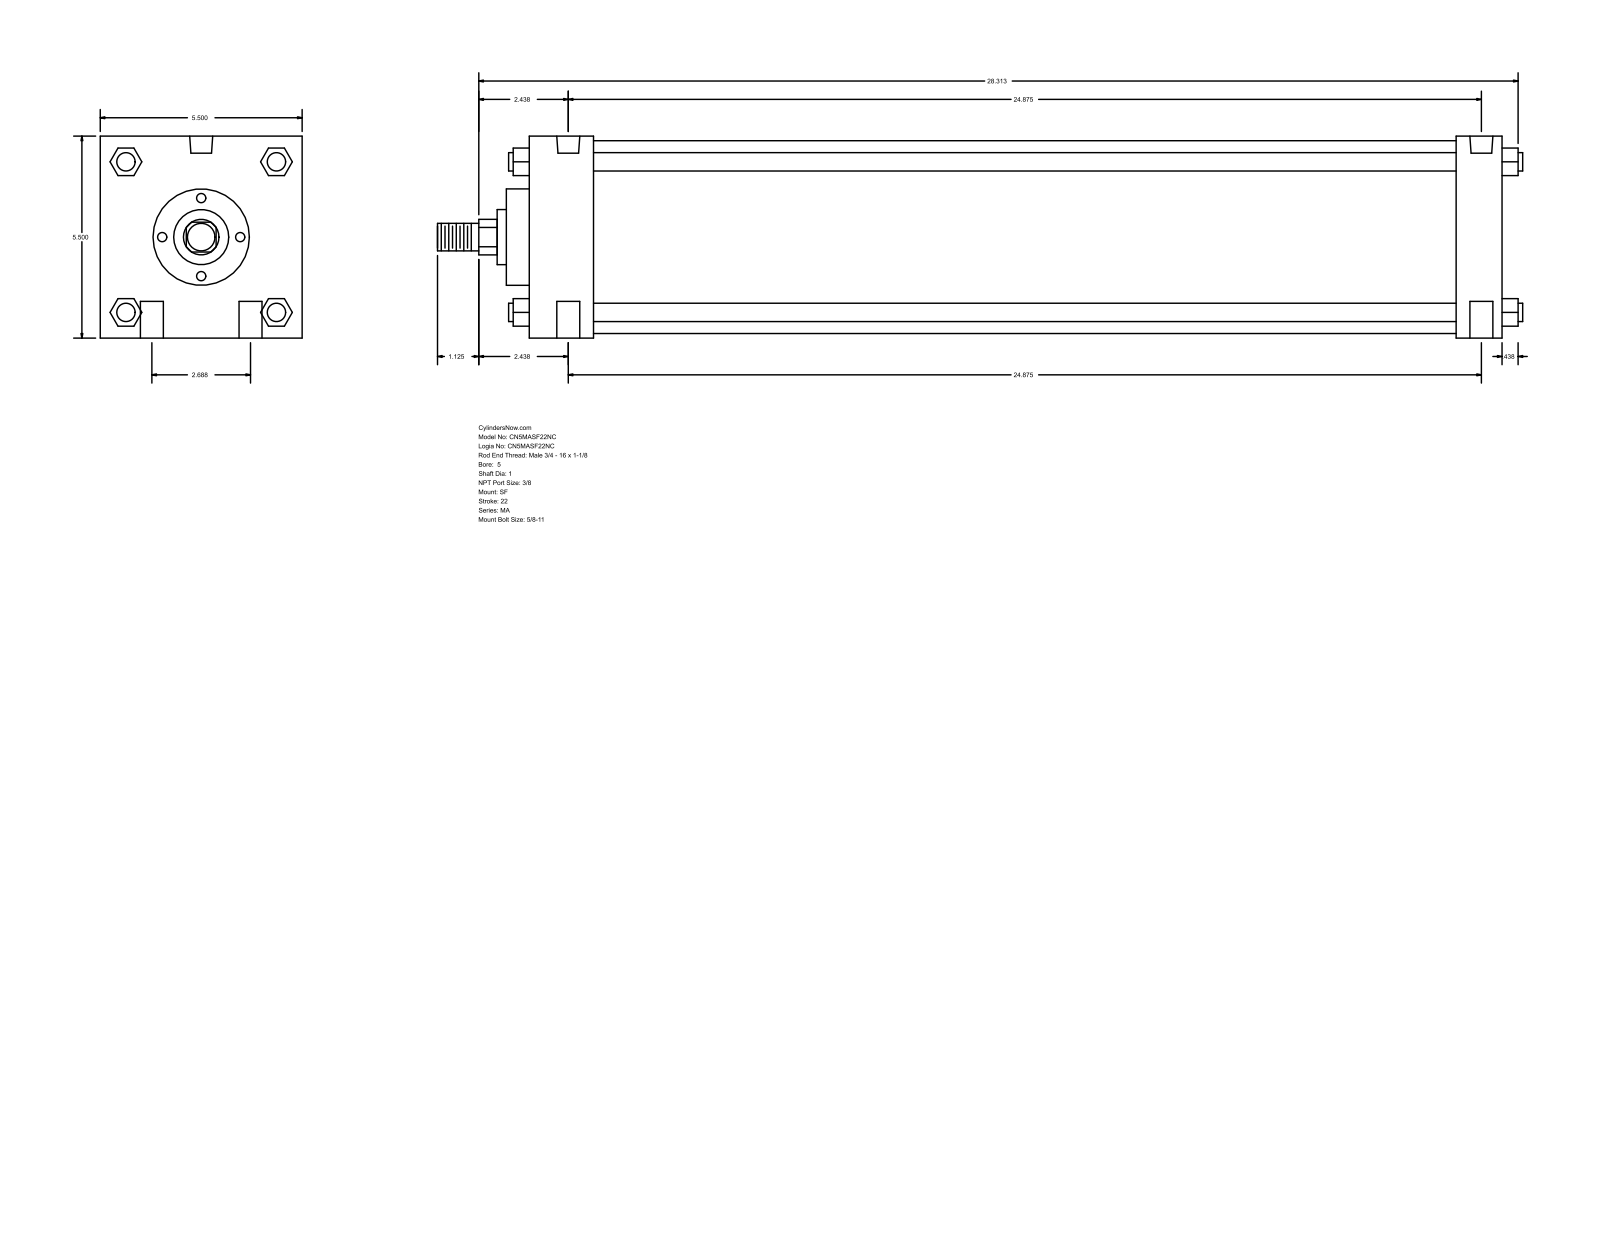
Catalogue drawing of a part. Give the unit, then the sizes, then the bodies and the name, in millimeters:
Units: millimetres
Overall size (bounding box): 750.89 × 139.7 × 139.7
Round holes (diameter × count): ⌀15.88 ×4, ⌀11.11 ×2, ⌀15.93 ×2
Round bosses / shafts (diameter × count): ⌀12.7 ×4, ⌀133.35 ×1, ⌀66.67 ×1, ⌀38.1 ×1, ⌀25.4 ×1, ⌀19.05 ×1
Partial cylindrical surfaces — rounded edges, fillets, slot ends (radius × count): R12.29 ×1
Main face-to-face distances: 139.7, 673.1, 44.46, 641.35, 596.89, 628.64, 31.75, 15.87, 60.33, 657.22
Hole centre spacings: 34.13, 632.75, 631.83, 68.26, 635.51, 622.31
Bodies: 0 solids, 126 faces (95 planar, 31 cylindrical, 0 other)
Part name (STEP PRODUCT): MA_SF__0500_1
STEP written by: GSSL Pune (CONFIG_CONTROL_DESIGN)
